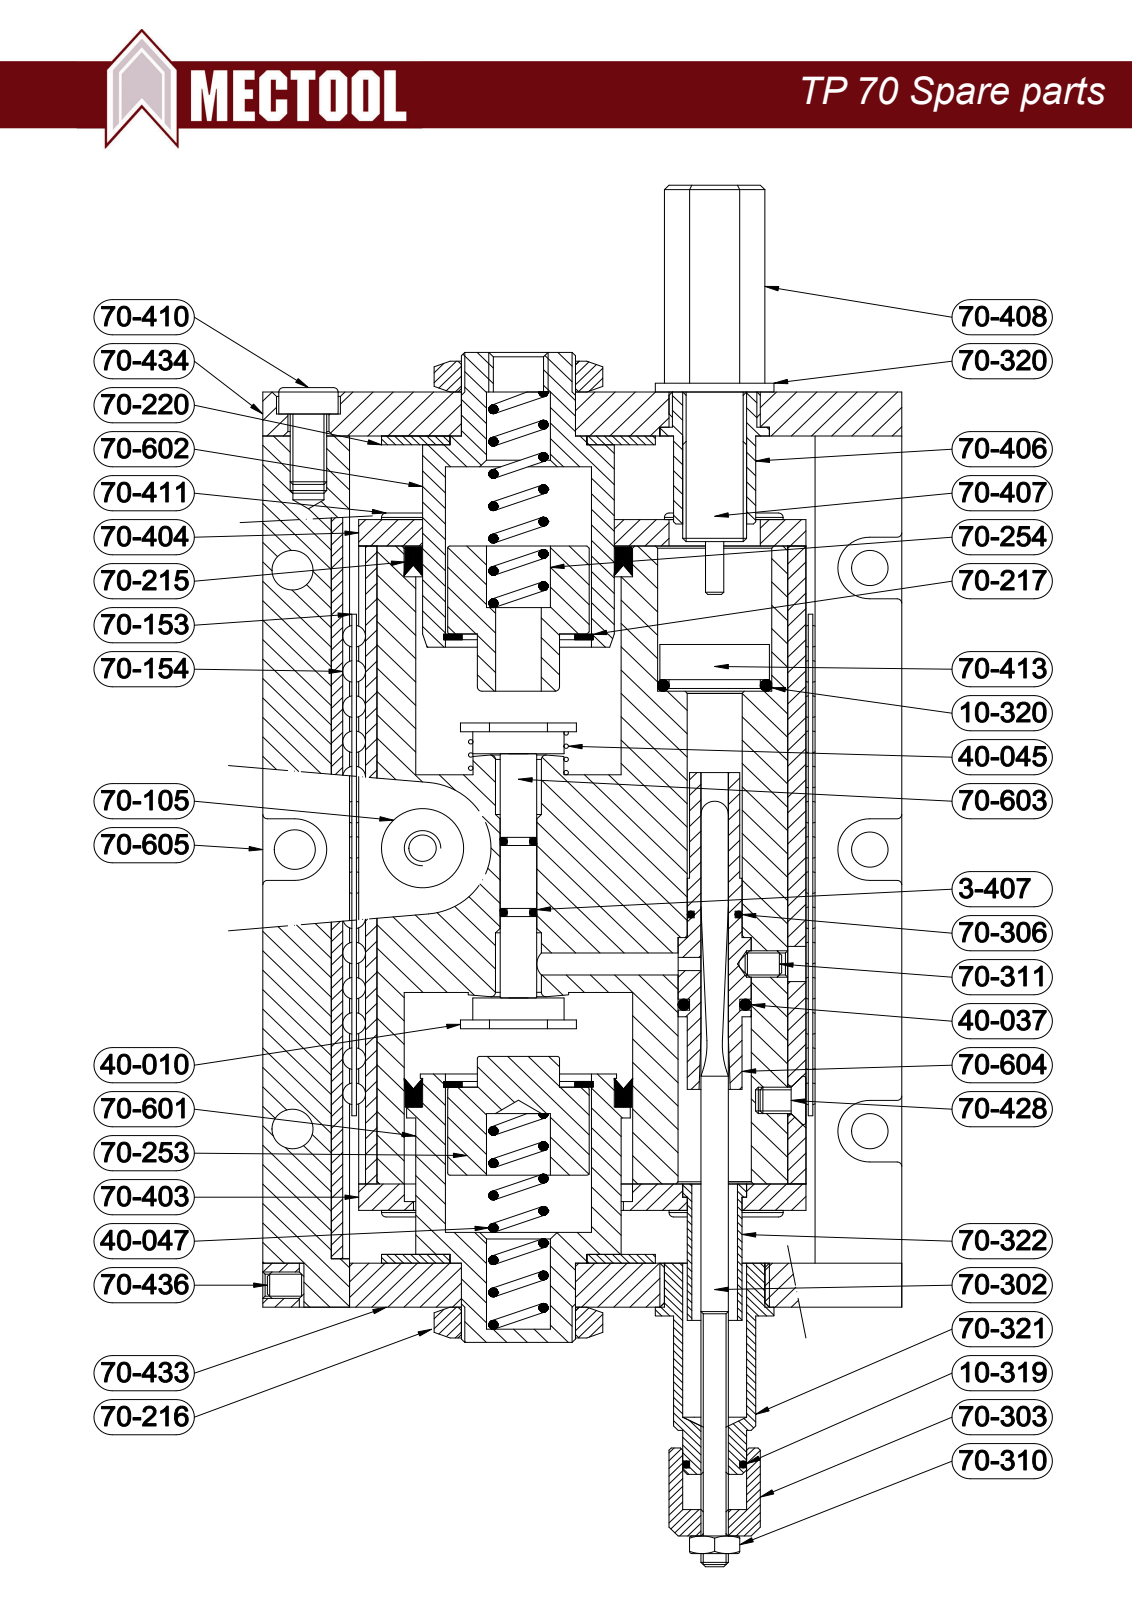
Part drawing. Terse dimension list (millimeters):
name: Bolt : Hex - M12,0 x 30,0; Nut : Standard - M22,0 x 266,7; Bolt : Hex - M22,0 x 30,0; Screw : Socket - M8,0 x 25,0 (+1 more)
written by: Spatial InterOp 3D (automotive_design)
unit: mm
bodies: 86 solids, 2832 faces (2425 planar, 282 cylindrical, 125 other)
size: 325 × 140 × 77
volume: 2 127 000 mm³; area: 358 219 mm²
holes: 13× ⌀9, 6× ⌀7, 6× ⌀18, 4× ⌀3.3, 4× ⌀13, 2× ⌀20, 1× ⌀5, 1× ⌀9.25, 1× ⌀19.5, 1× ⌀42, 1× ⌀46
bosses: 10× ⌀8, 6× ⌀4, 4× ⌀12.85, 1× ⌀60, 1× ⌀27, 1× ⌀25, 1× ⌀20, 1× ⌀19.5
rounds: 24× R0.77, 16× R1.5, 6× R7, 4× R5.5, 1× R9.8, 1× R10
face distances: 2, 19, 121, 10, 100, 21, 119, 198, 6, 75
hole spacings: 127, 60.6, 63.5, 140.26, 141.99, 70, 15, 17
